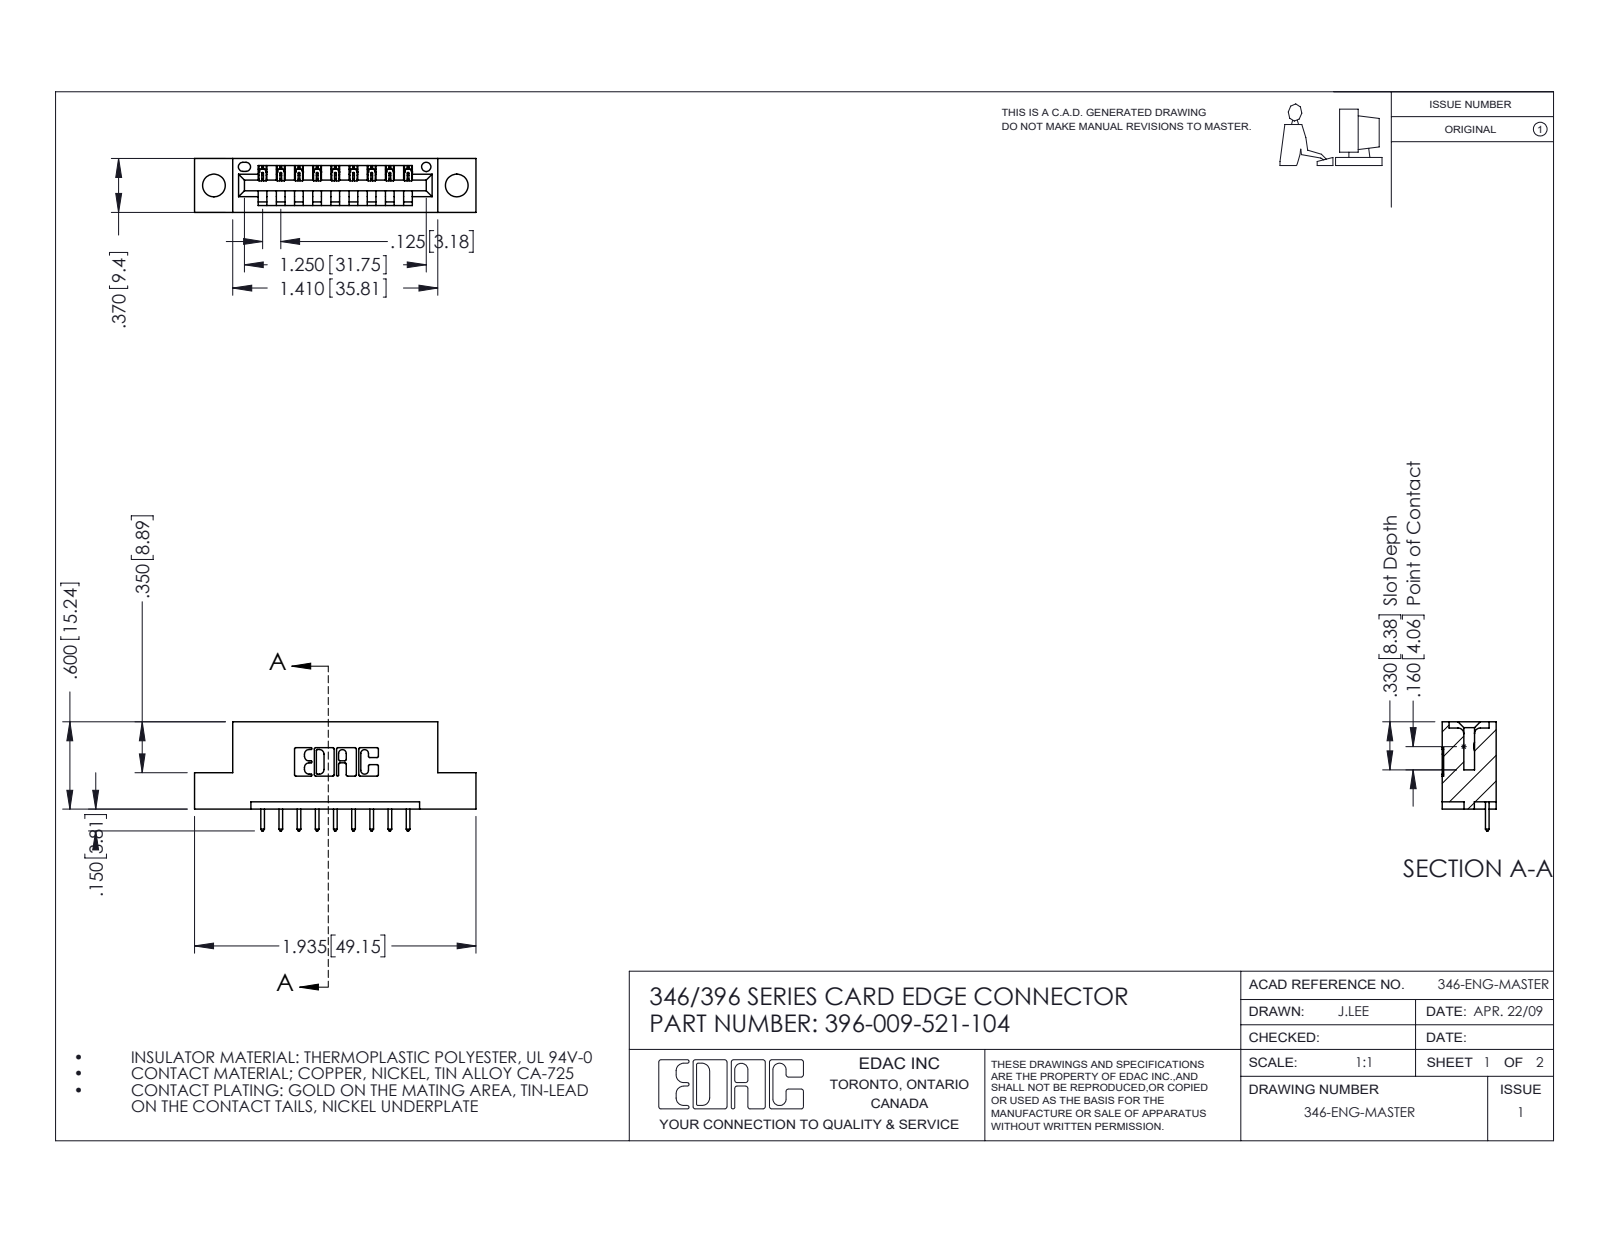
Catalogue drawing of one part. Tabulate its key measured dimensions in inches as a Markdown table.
| quantity | value |
| --- | --- |
| part name | 396-009-521-104; 345-292-001_345-293-121; 346 Part_Flush Mounting Lugs - 0.156 Dia-TH |
| STEP written by | SolidWorks 2016 (CONFIG_CONTROL_DESIGN) |
| units | inches |
| bodies | 10 solids, 644 faces (436 planar, 208 cylindrical, 0 other) |
| overall size | 1.935 × 0.75 × 0.37 |
| volume | 0.266 in³ |
| surface area | 7.442 in² |
| round holes (diameter × count) | 0.156 × 2, 0.064 × 1 |
| partial cylindrical surfaces (radius × count) | 0.01 × 22, 0.006 × 18, 0.01 × 18, 0.007 × 6, 0.031 × 6, 0.026 × 3, 0.031 × 2, 0.04 × 2 |
| main face-to-face distances | 0.25, 0.37, 0.048, 0.322, 0.148, 0.222, 0.1, 0.174, 0.072, 0.298 |
| hole center spacings | 0.246, 1.465, 1.67 |
